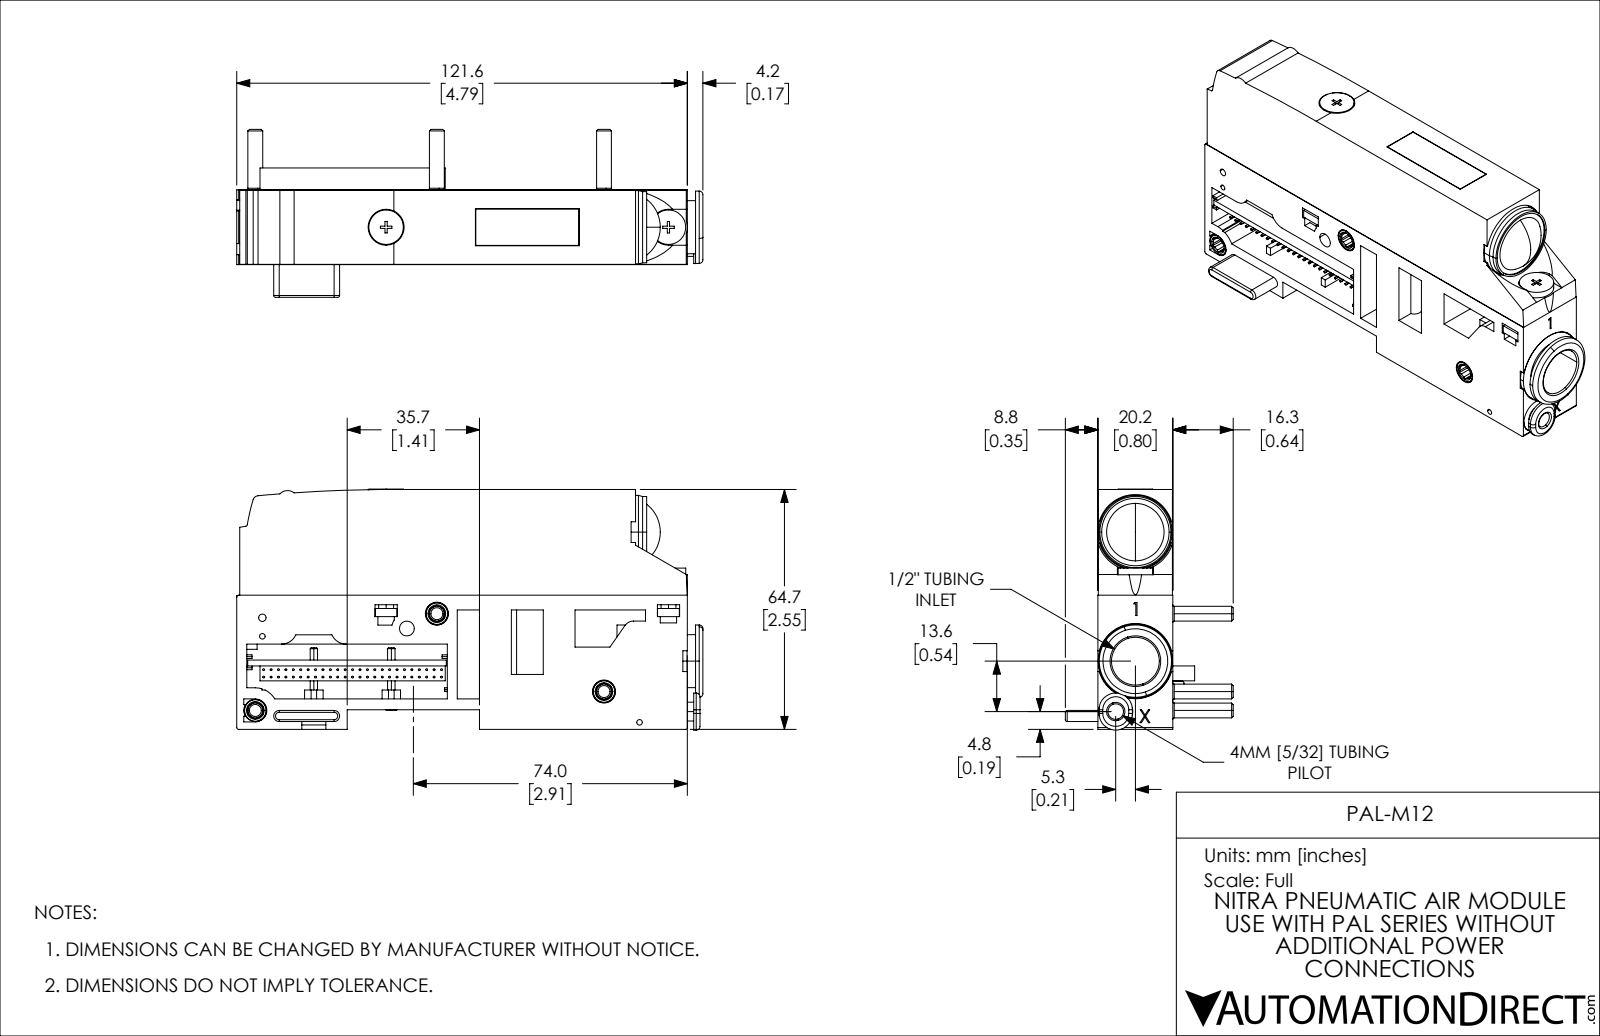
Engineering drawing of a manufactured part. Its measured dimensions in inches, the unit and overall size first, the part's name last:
Units: inches
Overall size (bounding box): 4.953 × 2.559 × 1.783
Round holes (diameter × count): ⌀0.02 ×50, ⌀0.128 ×3, ⌀0.157 ×3, ⌀0.165 ×3, ⌀0.059 ×2, ⌀0.079 ×2, ⌀0.094 ×2, ⌀0.177 ×2, ⌀0.244 ×2, ⌀0.126 ×1, ⌀0.189 ×1, ⌀0.362 ×1
Round bosses / shafts (diameter × count): ⌀0.157 ×7, ⌀0.366 ×3, ⌀0.236 ×3, ⌀0.079 ×2, ⌀0.787 ×1, ⌀0.78 ×1, ⌀0.768 ×1, ⌀0.756 ×1
Partial cylindrical surfaces — rounded edges, fillets, slot ends (radius × count): R0.007 ×12, R0.02 ×11, R0.007 ×8, R0.007 ×4, R0.039 ×4, R0.059 ×3, R0.082 ×3, R0.031 ×2
Main face-to-face distances: 0.791, 0.787, 0.795, 2.547, 0.323, 0.232, 0.697, 0.673, 0.583, 1.642
Hole centre spacings: 0.079, 0.111, 0.157, 0.176, 0.236, 0.249, 0.315, 0.325
Volume: 7.623 in³ · Surface area: 64.23 in²
Bodies: 4 solids, 1497 faces (1026 planar, 401 cylindrical, 70 other)
Part name (STEP PRODUCT): PAL-M12
STEP written by: SolidWorks 2019 (CONFIG_CONTROL_DESIGN)
